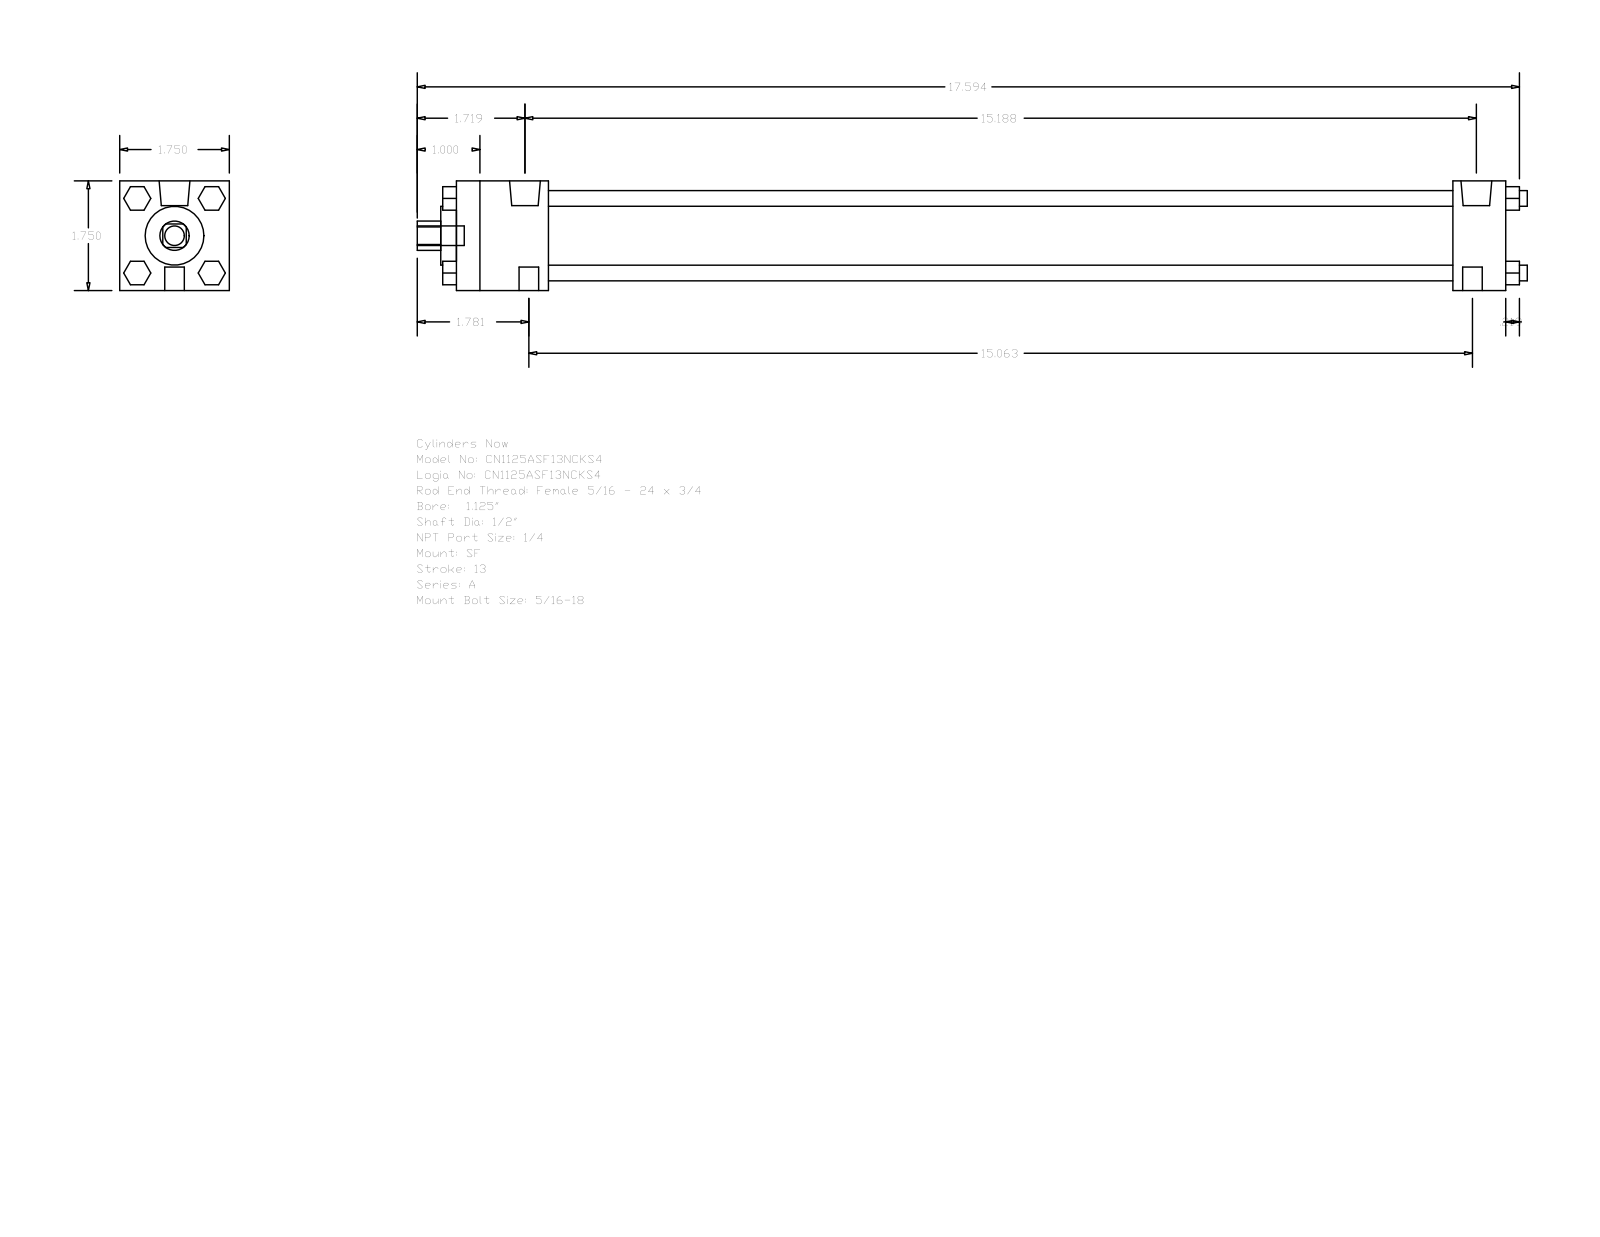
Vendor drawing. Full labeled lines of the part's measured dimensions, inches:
Part name (STEP PRODUCT): A_SF__0112_0.5
STEP written by: GSSL Pune (CONFIG_CONTROL_DESIGN)
Units: inches
Bodies: 0 solids, 120 faces (92 planar, 28 cylindrical, 0 other)
Overall size (bounding box): 17.719 × 1.75 × 1.75
Round holes (diameter × count): ⌀0.5 ×1, ⌀0.937 ×1, ⌀1.255 ×1
Round bosses / shafts (diameter × count): ⌀0.25 ×4, ⌀0.313 ×3, ⌀0.492 ×2, ⌀0.219 ×2
Partial cylindrical surfaces — rounded edges, fillets, slot ends (radius × count): R0.234 ×1
Main face-to-face distances: 1.75, 16.75, 15.906, 0.844, 1.469, 14.437, 15.281, 0.375, 0.22, 0.375
